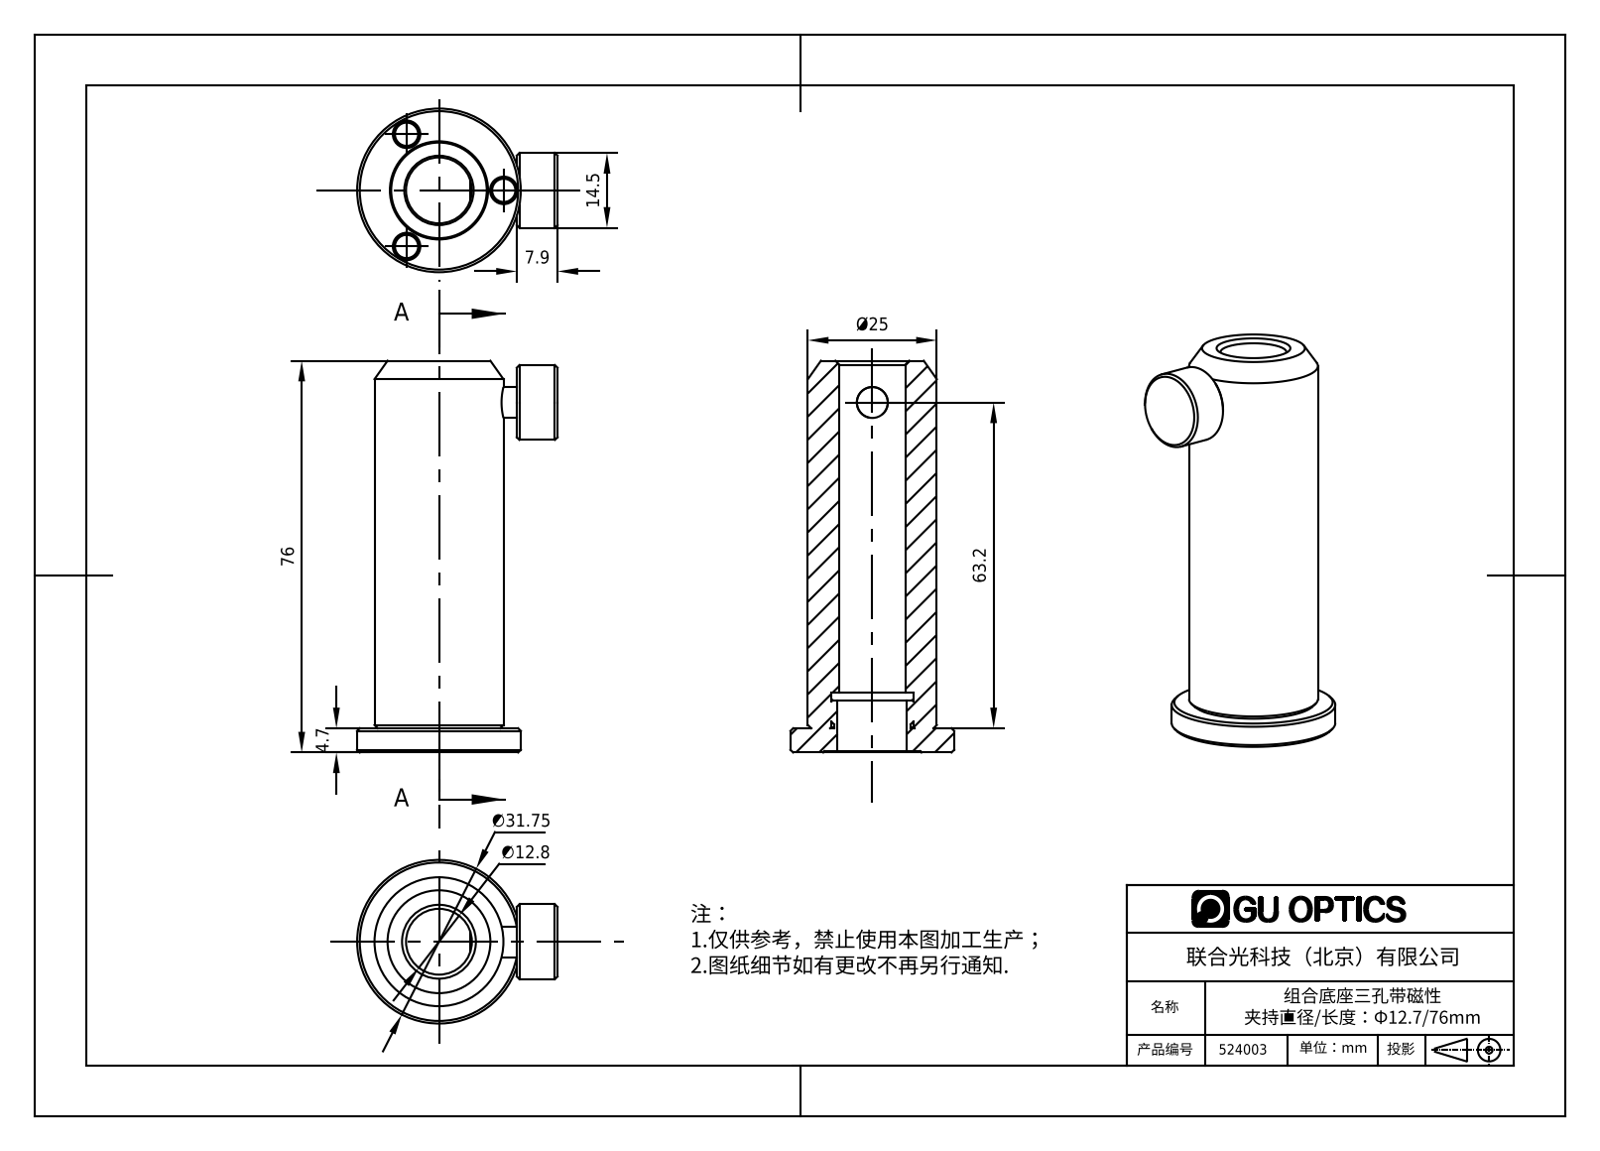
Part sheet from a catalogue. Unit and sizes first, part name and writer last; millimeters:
Units: millimetres
Overall size (bounding box): 76 × 38.88 × 31.75
Round holes (diameter × count): ⌀4.83 ×3, ⌀6 ×1, ⌀12.78 ×1, ⌀13.46 ×1, ⌀15.87 ×1
Round bosses / shafts (diameter × count): ⌀4.76 ×3, ⌀31.75 ×1, ⌀25.01 ×1, ⌀14.86 ×1, ⌀14.5 ×1
Partial cylindrical surfaces — rounded edges, fillets, slot ends (radius × count): R7.94 ×1
Main face-to-face distances: 4.7, 76, 71.3, 4.44, 75.74, 7.9, 11.56, 11.3, 6.86, 64.44
Hole centre spacings: 21.78, 12.58, 12.57
Volume: 29 687 mm³ · Surface area: 12 101 mm²
Bodies: 5 solids, 90 faces (19 planar, 31 cylindrical, 40 other)
Part name (STEP PRODUCT): 524003
STEP written by: SolidWorks 2016 (AUTOMOTIVE_DESIGN)
